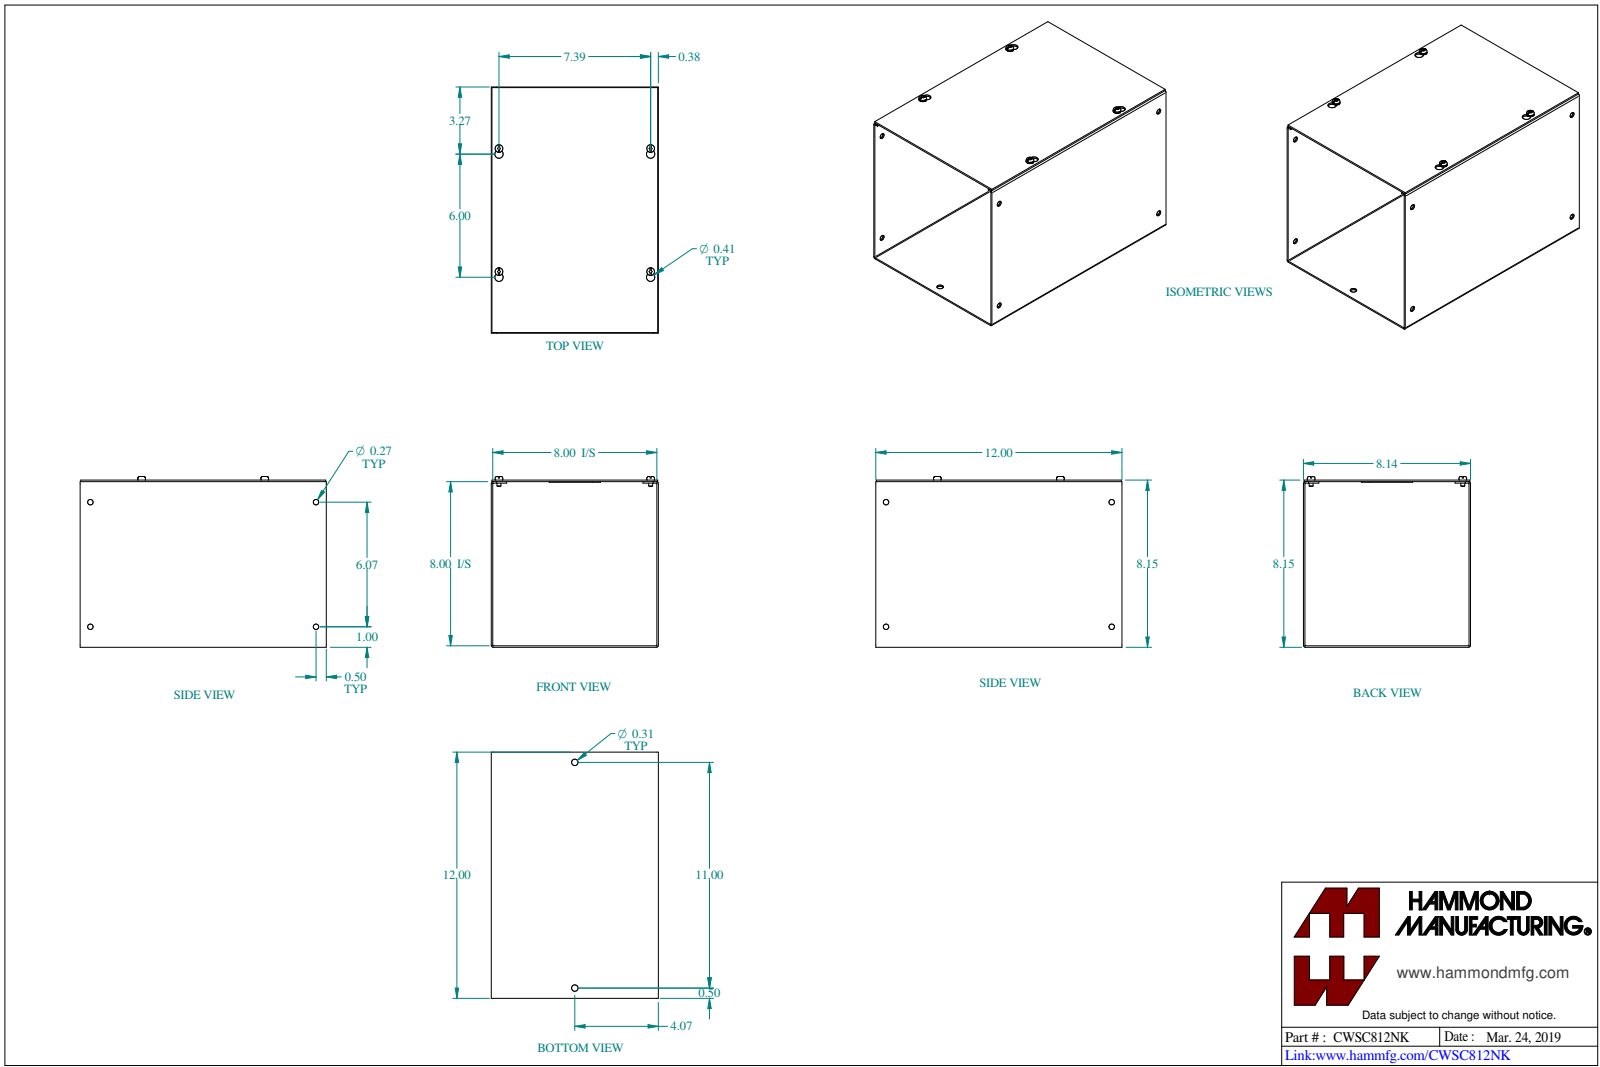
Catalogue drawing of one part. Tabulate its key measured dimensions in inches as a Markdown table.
| quantity | value |
| --- | --- |
| part name | CWSC812NK |
| STEP written by | SolidWorks 2023 (CONFIG_CONTROL_DESIGN) |
| units | inches |
| bodies | 6 solids, 180 faces (88 planar, 68 cylindrical, 24 other) |
| overall size | 12 × 8.325 × 8.144 |
| volume | 29.29 in³ |
| surface area | 807.2 in² |
| round holes (diameter × count) | 0.177 × 4, 0.266 × 4, 0.313 × 2 |
| round bosses / shafts (diameter × count) | 0.375 × 4, 0.19 × 4 |
| partial cylindrical surfaces (radius × count) | 0.036 × 4, 0.108 × 4, 0.125 × 4, 0.203 × 4 |
| main face-to-face distances | 0.072, 8.072, 8, 0.078, 8.15, 8.078, 8.144, 7.928, 0.15, 0.031 |
| hole center spacings | 4.463, 9.269, 11, 6, 6.072, 7.394, 9.522, 12.565 |
